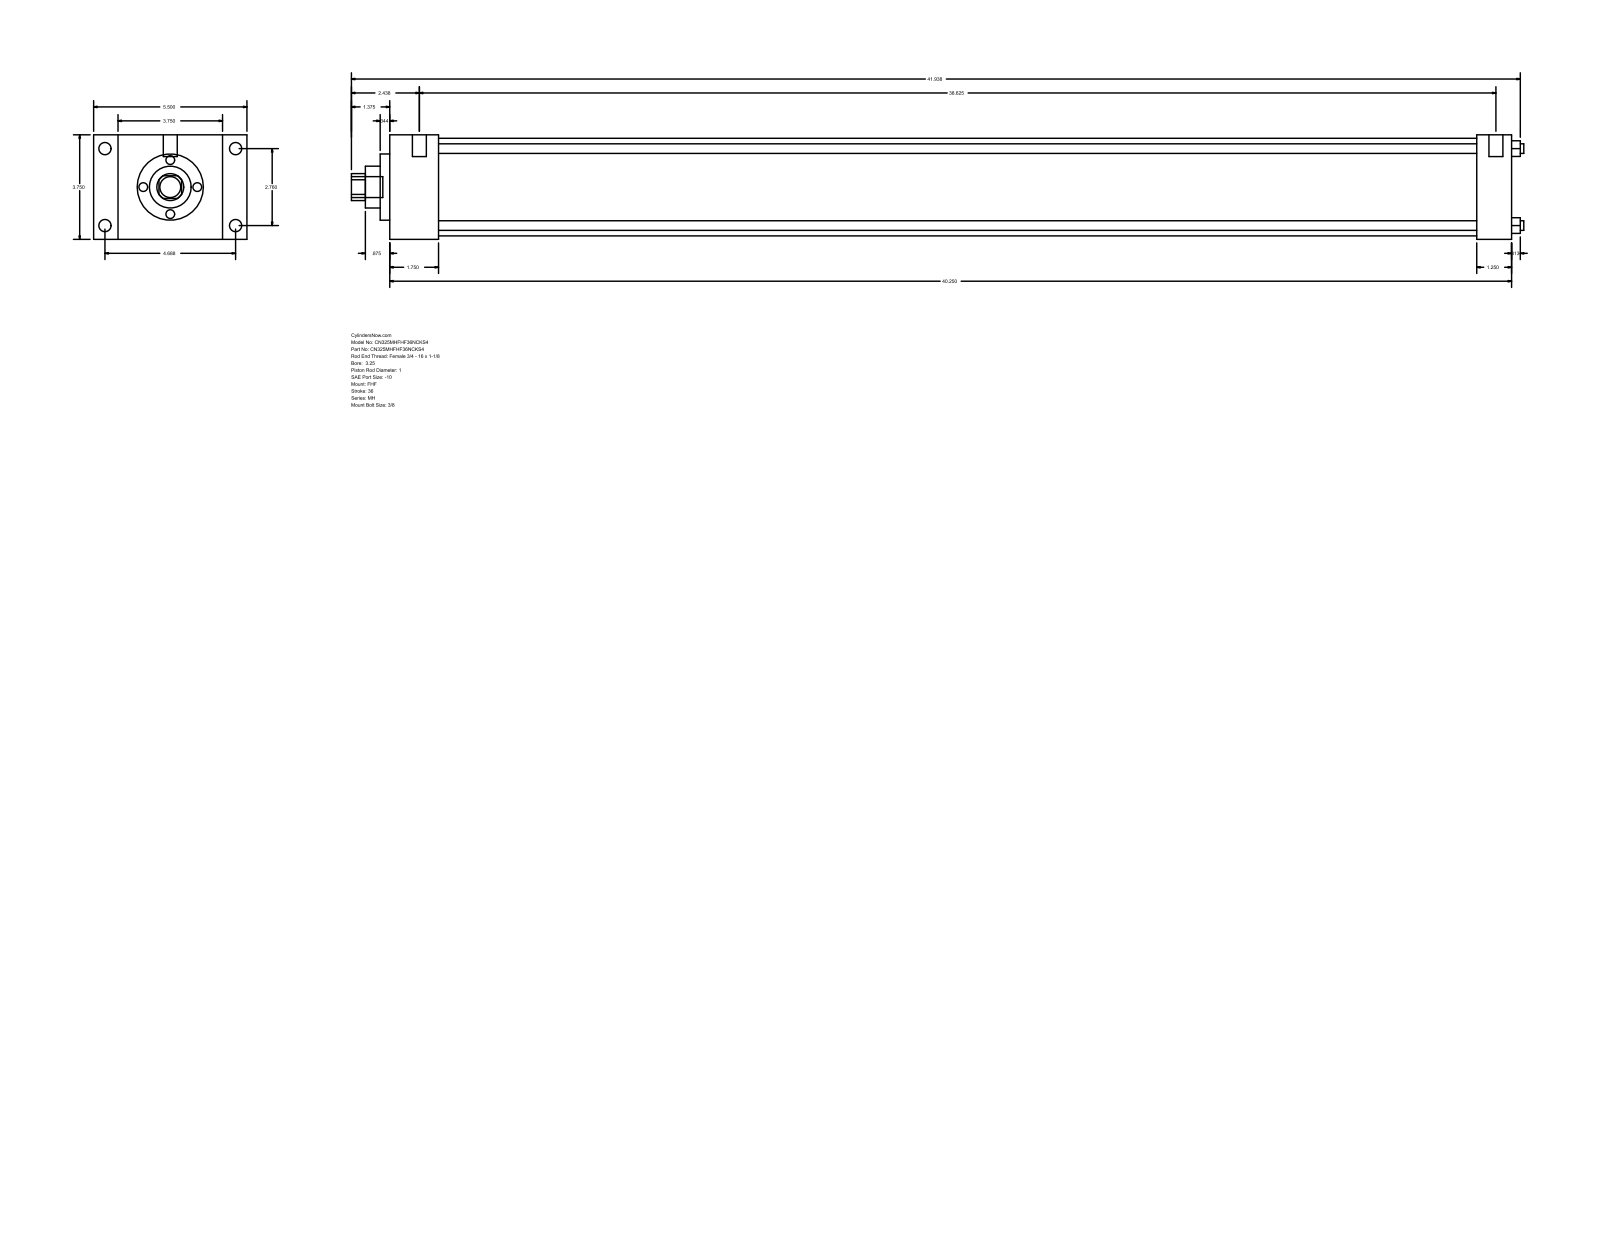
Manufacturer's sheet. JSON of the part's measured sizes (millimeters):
{"part_name": "MH_FHF__0325_1", "step_written_by": "GSSL Pune (CONFIG_CONTROL_DESIGN)", "units": "millimeters", "bodies": {"solids": 0, "faces": 90, "planar": 61, "cylindrical": 29, "other": 0}, "overall_size": [1068.39, 139.7, 95.25], "round_holes": [[8.76, 4], [25.4, 1], [38.1, 1], [60.33, 1], [88.9, 1]], "round_bosses_or_shafts": [[11.13, 4], [5.56, 4], [12.7, 2], [19.05, 1]], "partial_cylinders_radius": [[12.29, 1]], "face_to_face_distances": [95.24, 1022.36, 44.46, 977.9, 22.23, 117.47, 139.7, 990.61, 946.15, 31.75], "hole_center_spacings": [49.57, 70.1, 99.14]}
